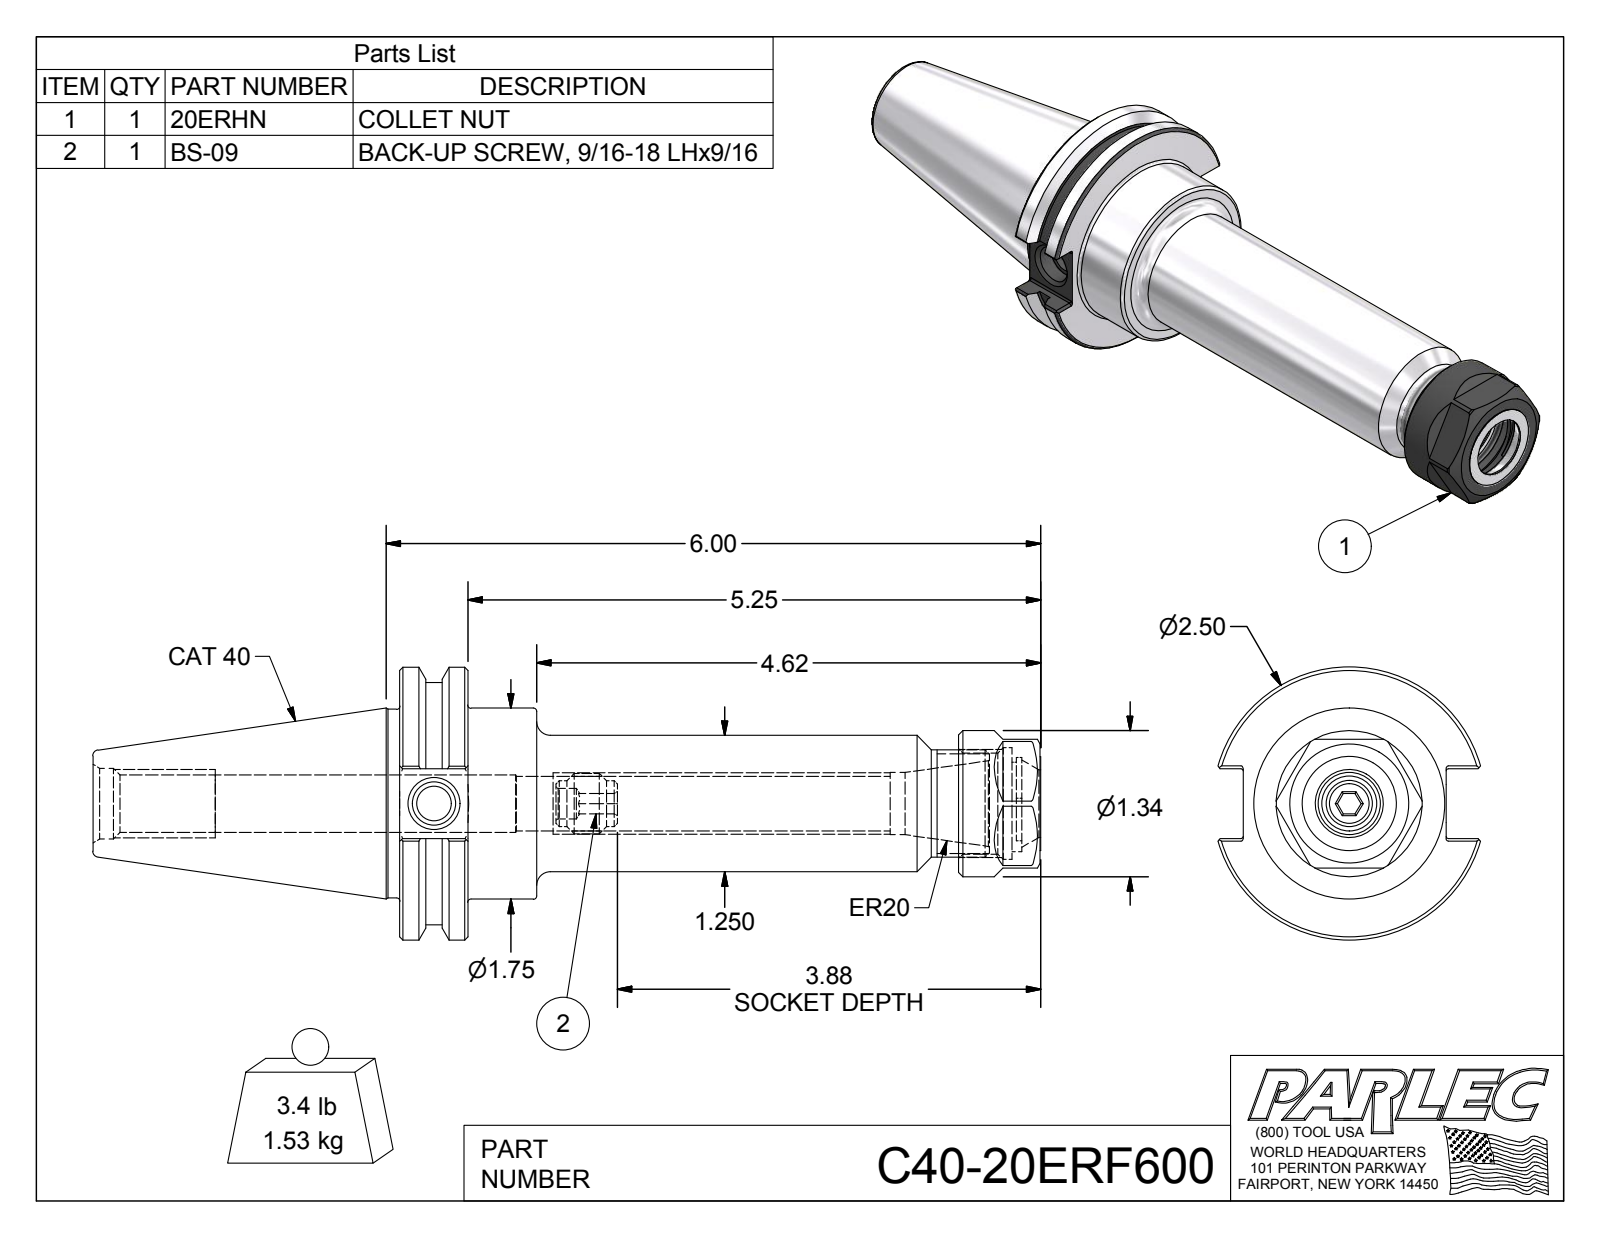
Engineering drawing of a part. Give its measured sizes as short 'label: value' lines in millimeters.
name: C40-20ER6-1; 20ERHN; BS-09; C40-20ERF600
written by: Autodesk Inventor 2016 (AUTOMOTIVE_DESIGN)
unit: mm
bodies: 3 solids, 146 faces (64 planar, 40 cylindrical, 42 other)
size: 220.66 × 63.5 × 61.05
volume: 196 012 mm³; area: 42 830 mm²
holes: 1× ⌀7.14, 1× ⌀8, 1× ⌀10.13, 1× ⌀12.75, 1× ⌀13.36, 1× ⌀13.39, 1× ⌀14.48, 1× ⌀15.49, 1× ⌀16.46, 1× ⌀23.5, 1× ⌀26
bosses: 1× ⌀63.5, 1× ⌀56.36, 1× ⌀44.45, 1× ⌀43.94, 1× ⌀34, 1× ⌀31.75, 1× ⌀25, 1× ⌀14.1
rounds: 12× R0.51, 1× R9.47, 1× R10.55, 1× R10.75
face distances: 15.88, 149.23, 133.35, 30, 31.88, 16, 117.35, 130.16, 114.28, 98.28
